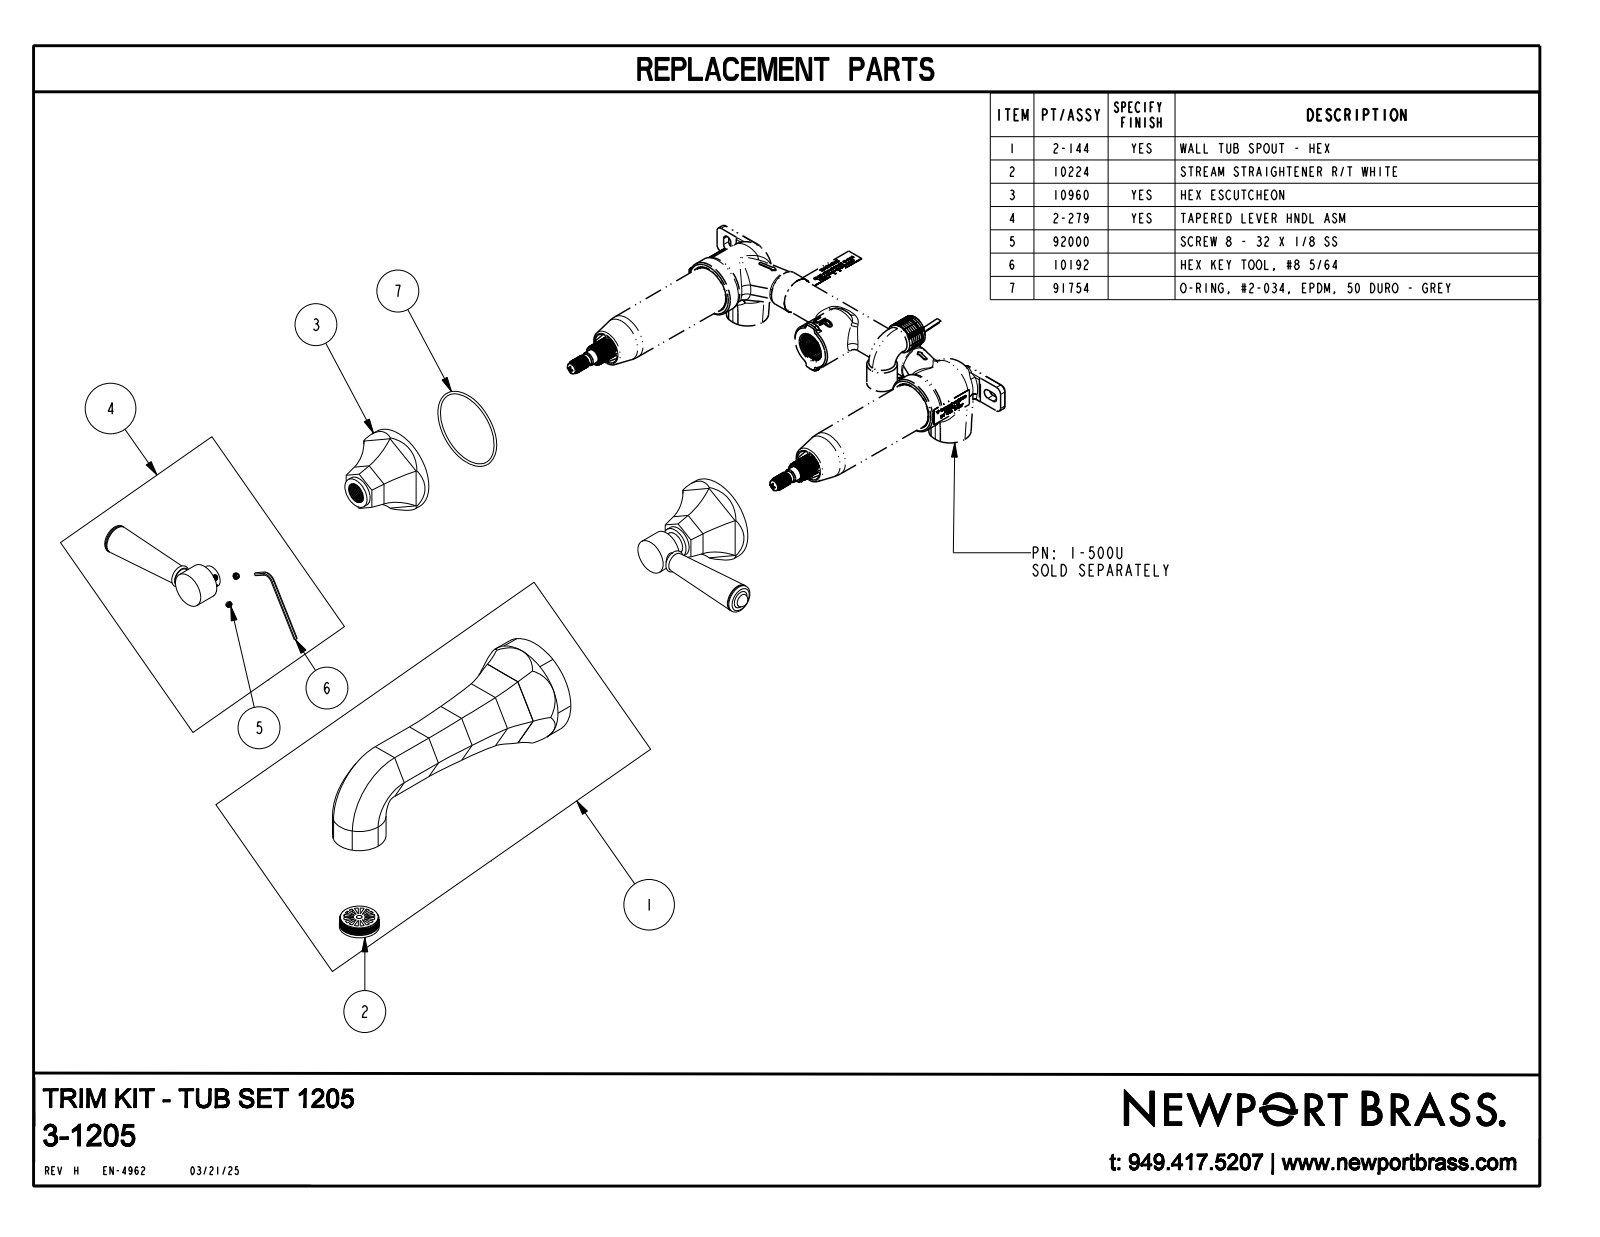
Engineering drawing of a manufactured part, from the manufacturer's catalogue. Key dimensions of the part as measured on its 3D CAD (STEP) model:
Part name (STEP PRODUCT): 3-1205_SW0002
STEP written by: CREO PARAMETRIC BY PTC INC, 2018400 (AUTOMOTIVE_DESIGN)
Units: inches
Bodies: 3 solids, 178 faces (46 planar, 54 cylindrical, 78 other)
Overall size (bounding box): 14.66 × 8.833 × 7.562
Volume: 28.67 in³ · Surface area: 101.4 in²
Round holes (diameter × count): ⌀0.385 ×1
Round bosses / shafts (diameter × count): ⌀2.375 ×2, ⌀0.98 ×2, ⌀0.86 ×2, ⌀0.625 ×2, ⌀2.8 ×1, ⌀0.792 ×1, ⌀0.365 ×1
Partial cylindrical surfaces — rounded edges, fillets, slot ends (radius × count): R1.541 ×10, R2.125 ×6
Main face-to-face distances: 1.299, 0.995, 2.294, 6.693, 1.962, 4.764, 1.527, 0.435, 1.647, 0.12
